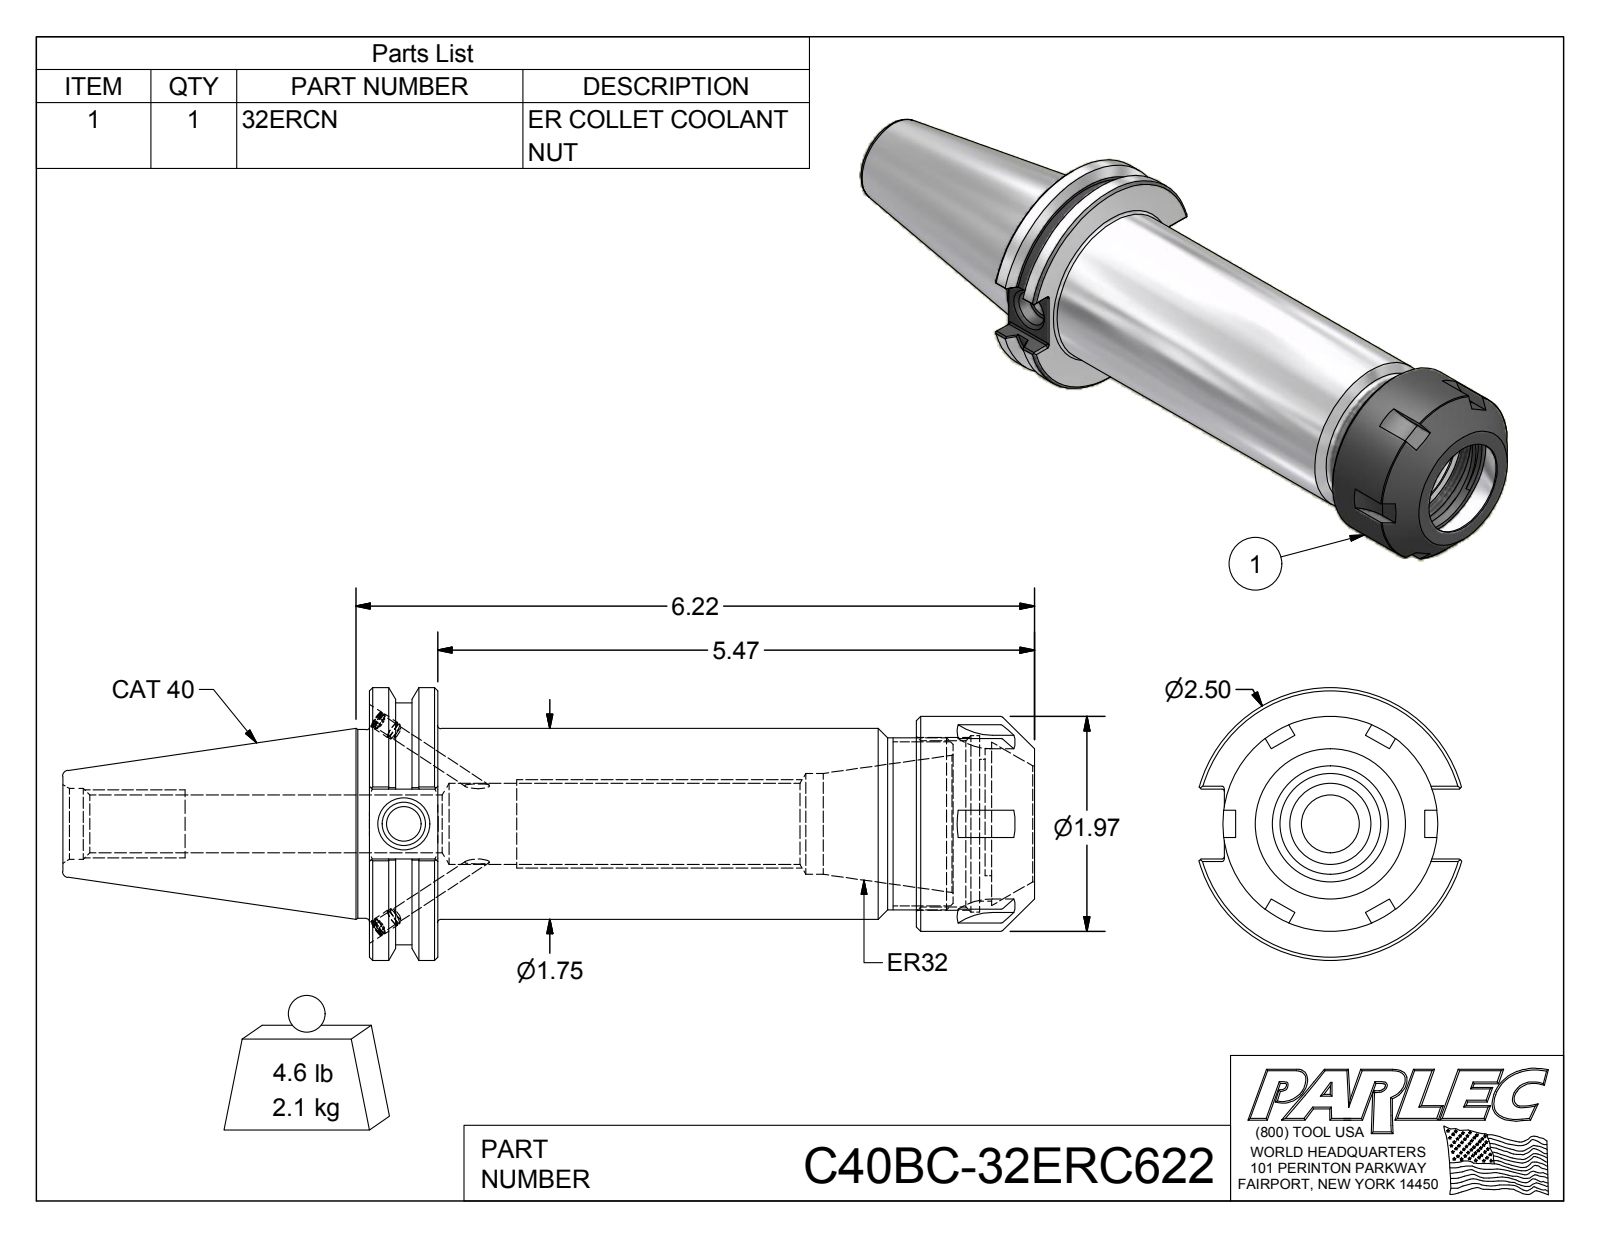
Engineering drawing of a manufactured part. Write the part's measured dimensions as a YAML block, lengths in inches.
part_name: "C40BC-32ERC622; C40BCB-32ER6-1; 029-965; 32ERCN"
step_written_by: "Autodesk Inventor 2012 (AUTOMOTIVE_DESIGN)"
units: inches
bodies: {solids: 4, faces: 173, planar: 76, cylindrical: 49, other: 48}
overall_size: [8.907, 2.5, 2.406]
volume: 15.71
surface_area: 84.71
round_holes:
  - {diameter: 0.13, count: 2}
  - {diameter: 0.161, count: 2}
  - {diameter: 0.315, count: 1}
  - {diameter: 0.399, count: 1}
  - {diameter: 0.527, count: 1}
  - {diameter: 0.648, count: 1}
  - {diameter: 0.745, count: 1}
  - {diameter: 0.925, count: 1}
  - {diameter: 1.063, count: 1}
  - {diameter: 1.299, count: 1}
  - {diameter: 1.522, count: 1}
  - {diameter: 1.614, count: 1}
round_bosses_or_shafts:
  - {diameter: 0.165, count: 2}
  - {diameter: 0.157, count: 2}
  - {diameter: 2.5, count: 1}
  - {diameter: 2.219, count: 1}
  - {diameter: 1.969, count: 1}
  - {diameter: 1.75, count: 1}
  - {diameter: 1.73, count: 1}
  - {diameter: 1.575, count: 1}
partial_cylinders:
  - {radius: 0.02, count: 12}
  - {radius: 0.5, count: 6}
  - {radius: 0.689, count: 1}
face_to_face_distances: [0.625, 5.012, 4.387, 5.591, 4.966, 0.579, 6.095, 5.47, 1.083, 0.504]
hole_center_spacings: [0.059]
